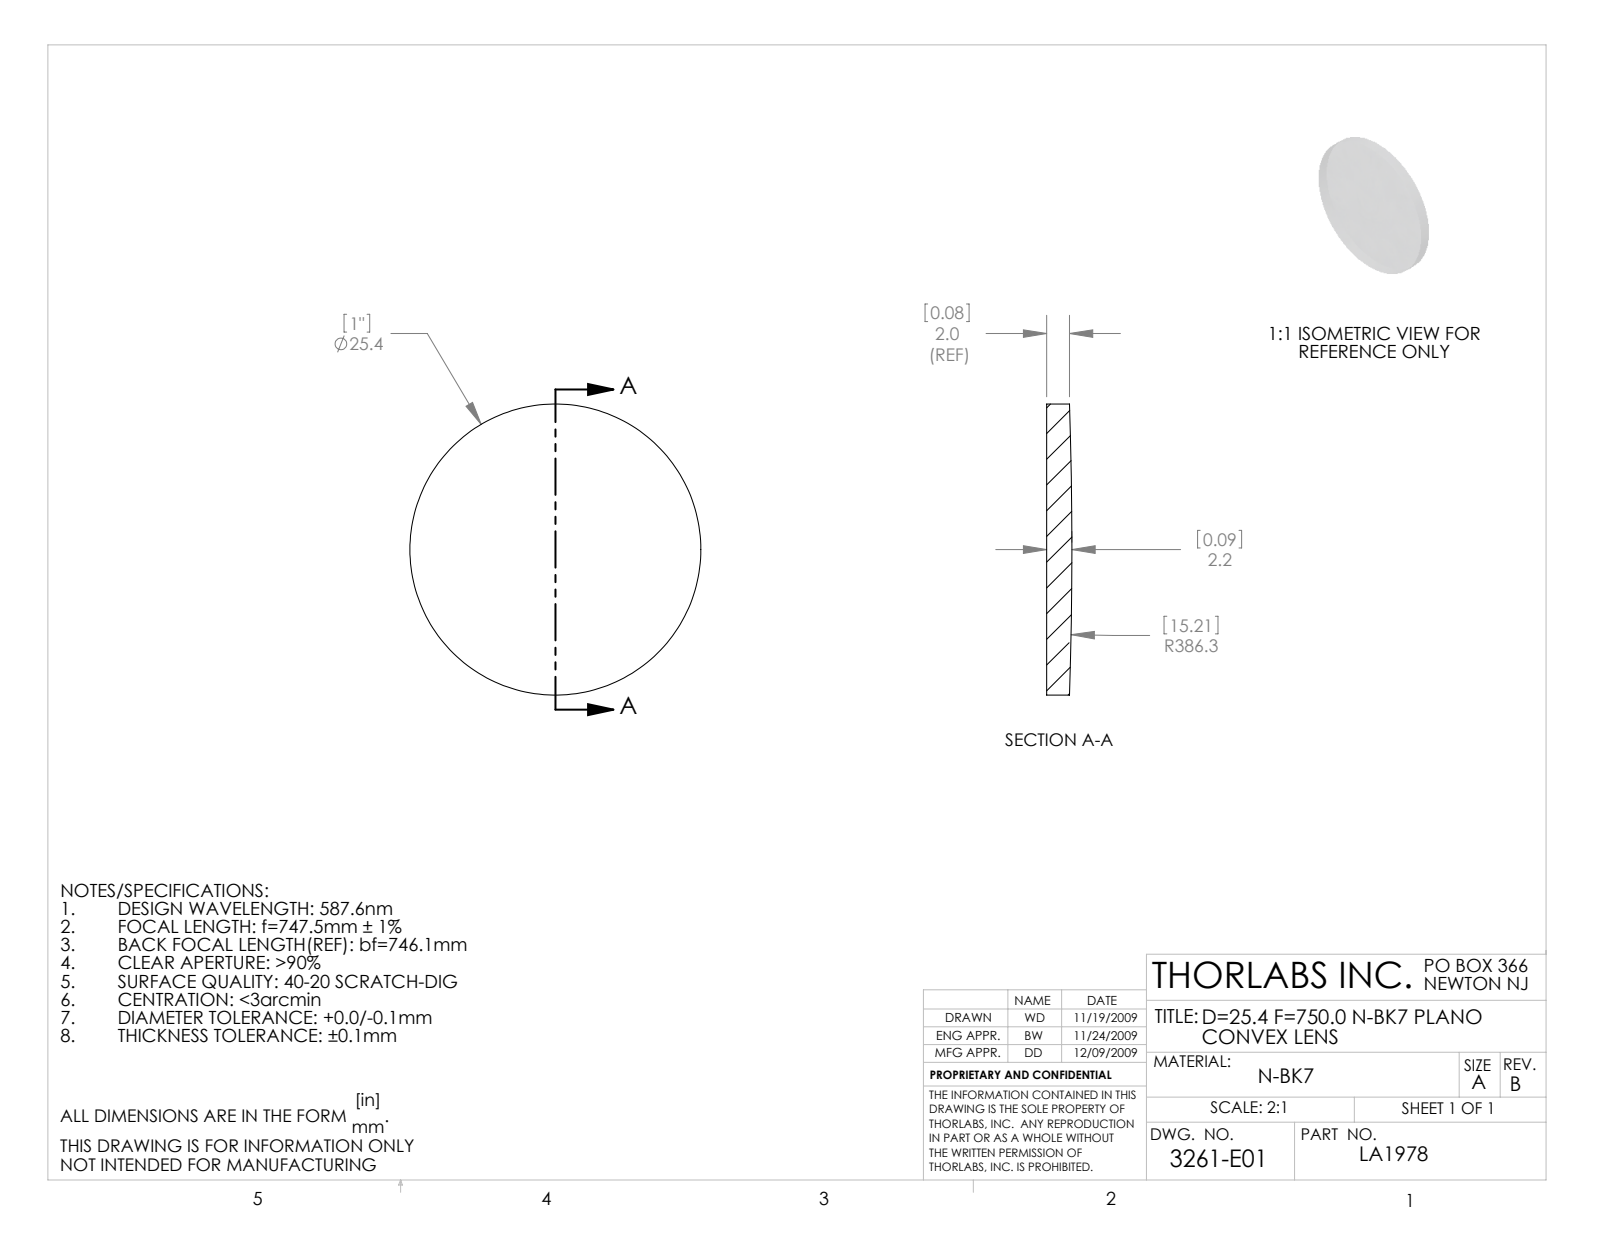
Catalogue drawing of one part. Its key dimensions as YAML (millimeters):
part_name: "3261-E0W"
step_written_by: "SolidWorks 2009 (AUTOMOTIVE_DESIGN)"
units: millimeters
bodies: {solids: 1, faces: 5, planar: 1, cylindrical: 2, other: 2}
overall_size: [25.4, 25.4, 2.2]
volume: 1062
surface_area: 1172
round_bosses_or_shafts:
  - {diameter: 25.4, count: 1}
